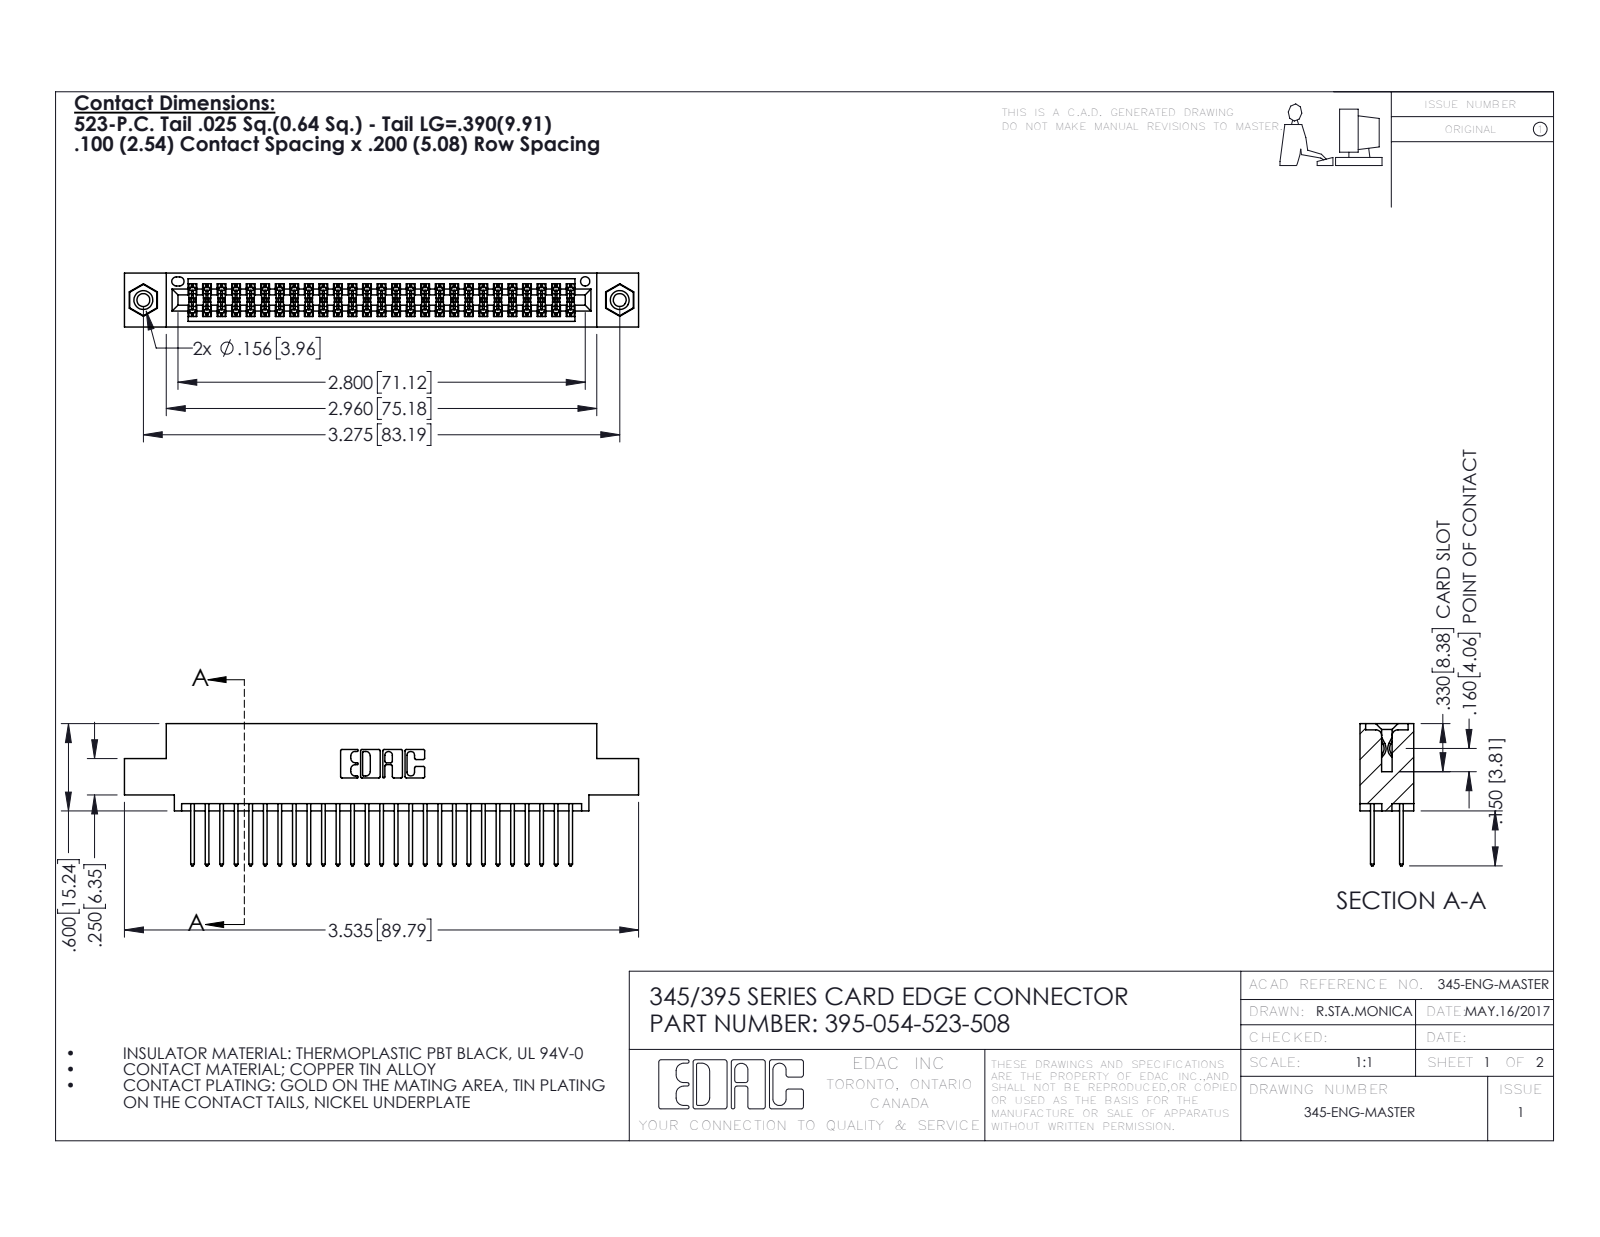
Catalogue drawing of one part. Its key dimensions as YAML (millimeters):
part_name: "345-292-001_345-293-123; 345-250-001_345-250-003-102; 345 Part_0.110 Offset - 0.156 Dia-TI; 395-054-523-508"
step_written_by: "SolidWorks 2016 (CONFIG_CONTROL_DESIGN)"
units: millimeters
bodies: {solids: 57, faces: 2890, planar: 1898, cylindrical: 976, other: 16}
overall_size: [89.8, 24.8, 9.4]
volume: 8620
surface_area: 13050
round_holes:
  - {diameter: 2.3, count: 2}
  - {diameter: 3.2, count: 2}
  - {diameter: 4, count: 2}
  - {diameter: 1.6, count: 1}
round_bosses_or_shafts:
  - {diameter: 3.9, count: 2}
partial_cylinders:
  - {radius: 0.2, count: 81}
  - {radius: 0.3, count: 54}
  - {radius: 0.3, count: 22}
  - {radius: 0.2, count: 6}
  - {radius: 0.8, count: 6}
  - {radius: 0.7, count: 3}
  - {radius: 0.4, count: 2}
  - {radius: 0.5, count: 2}
face_to_face_distances: [1.8, 7.6, 5.1, 2.5, 6.9, 0.6, 9.4, 5.7, 4.4, 3.8]
hole_center_spacings: [6.9, 77.2, 83.2]
